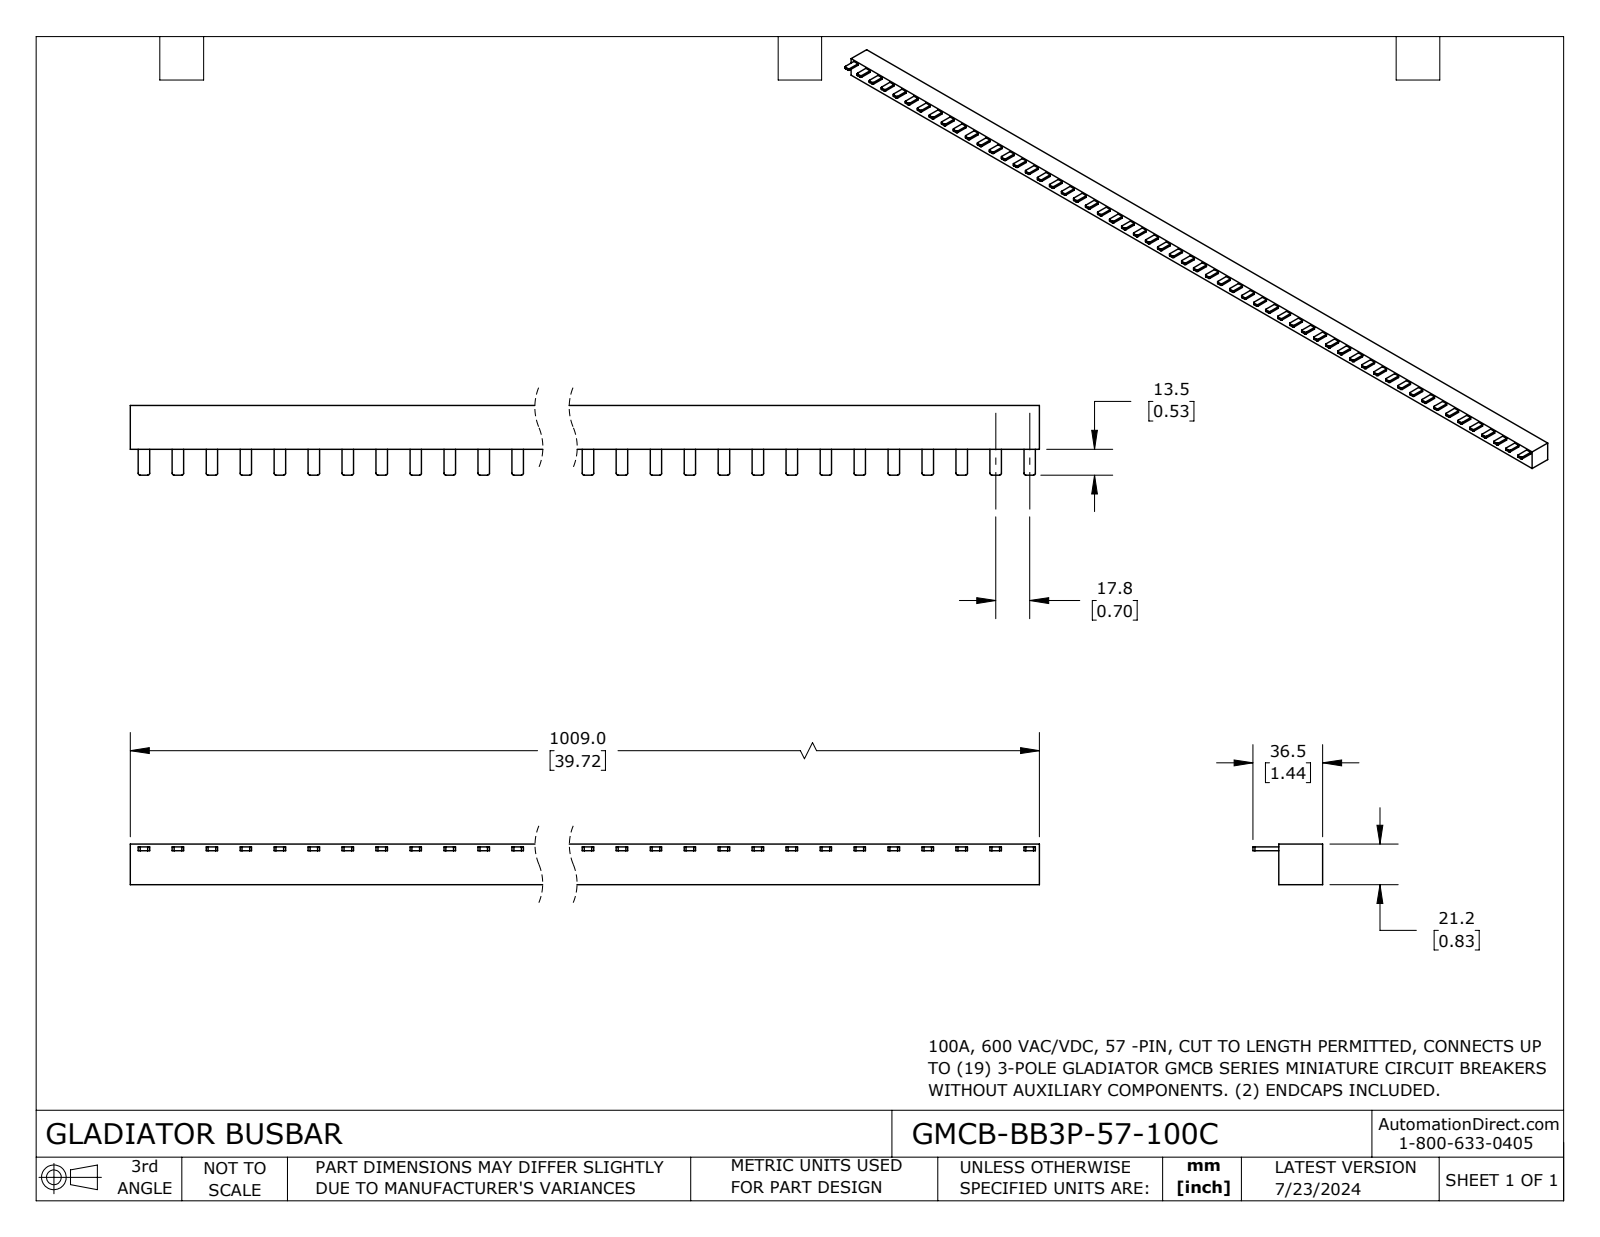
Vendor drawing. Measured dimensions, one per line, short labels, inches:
name: GMCB-BB3P-57-100C
written by: SolidWorks 2023 (CONFIG_CONTROL_DESIGN)
unit: in
bodies: 1 solid, 405 faces (291 planar, 114 cylindrical, 0 other)
size: 39.724 × 1.437 × 0.835
volume: 30.58 in³; area: 158.6 in²
rounds: 114× R0.039
face distances: 0.835, 0.906, 0.697, 0.138, 0.776, 0.079, 0.059, 39.724, 0.531, 1.437
